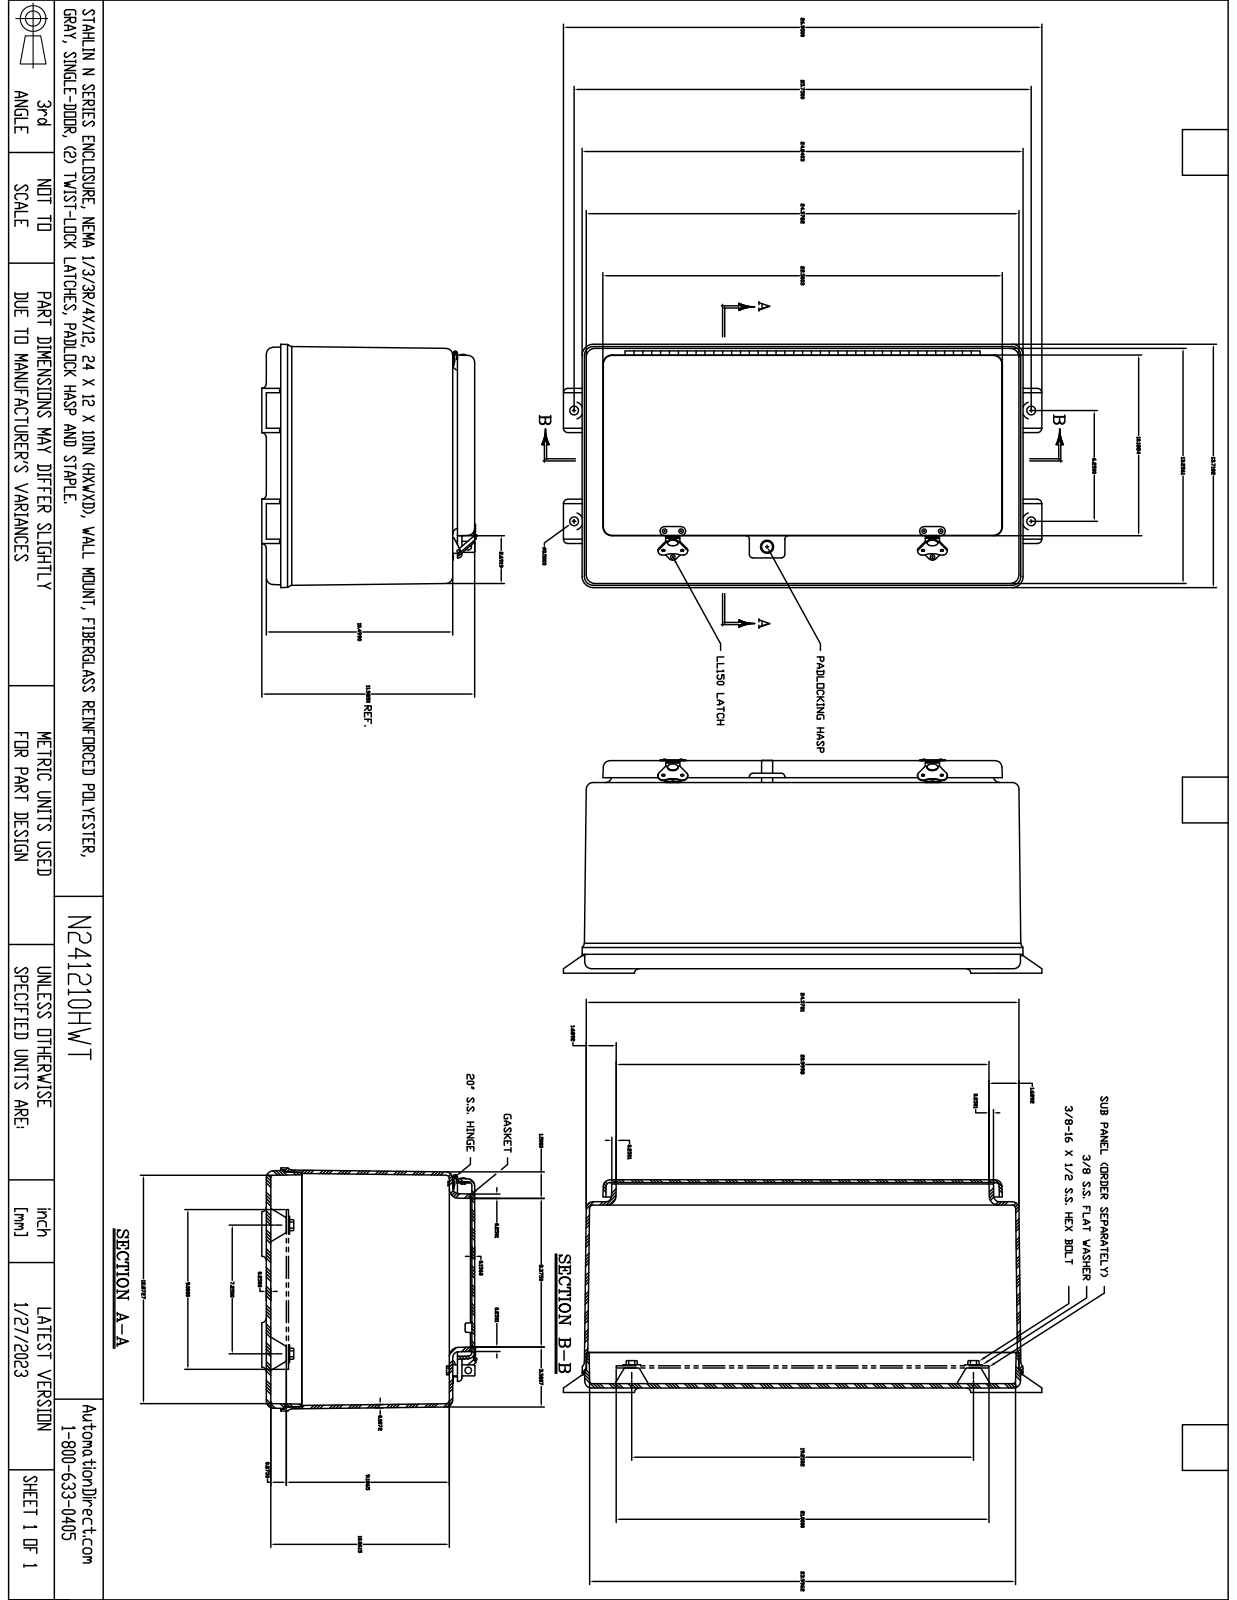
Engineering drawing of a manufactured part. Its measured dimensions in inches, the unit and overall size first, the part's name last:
Units: inches
Overall size (bounding box): 26.938 × 13.719 × 12.205
Round holes (diameter × count): ⌀0.13 ×21, ⌀0.063 ×8, ⌀0.065 ×6, ⌀0.138 ×4, ⌀0.187 ×4, ⌀0.563 ×4, ⌀0.065 ×2, ⌀0.145 ×2, ⌀0.281 ×2, ⌀0.51 ×2, ⌀0.51 ×2, ⌀0.125 ×1
Round bosses / shafts (diameter × count): ⌀0.297 ×8, ⌀0.14 ×8, ⌀0.5 ×2, ⌀0.281 ×1, ⌀0.25 ×1, ⌀0.201 ×1, ⌀0.2 ×1, ⌀0.135 ×1
Partial cylindrical surfaces — rounded edges, fillets, slot ends (radius × count): R0.01 ×59, R0.25 ×24, R0.188 ×14, R0.5 ×12, R0.375 ×10, R0.03 ×8, R0.313 ×8, R0.187 ×7
Main face-to-face distances: 0.187, 0.25, 0.156, 11.75, 11.5, 11.594, 11.344, 10.5, 10.313, 10.063
Hole centre spacings: 0.937, 1.482, 6.375, 12.625, 14.226, 14.625, 15.159, 14.625
Volume: 330.4 in³ · Surface area: 3 528 in²
Bodies: 38 solids, 1140 faces (443 planar, 446 cylindrical, 251 other)
Part name (STEP PRODUCT): T241210HWT
STEP written by: SolidWorks 2018 (AUTOMOTIVE_DESIGN)
